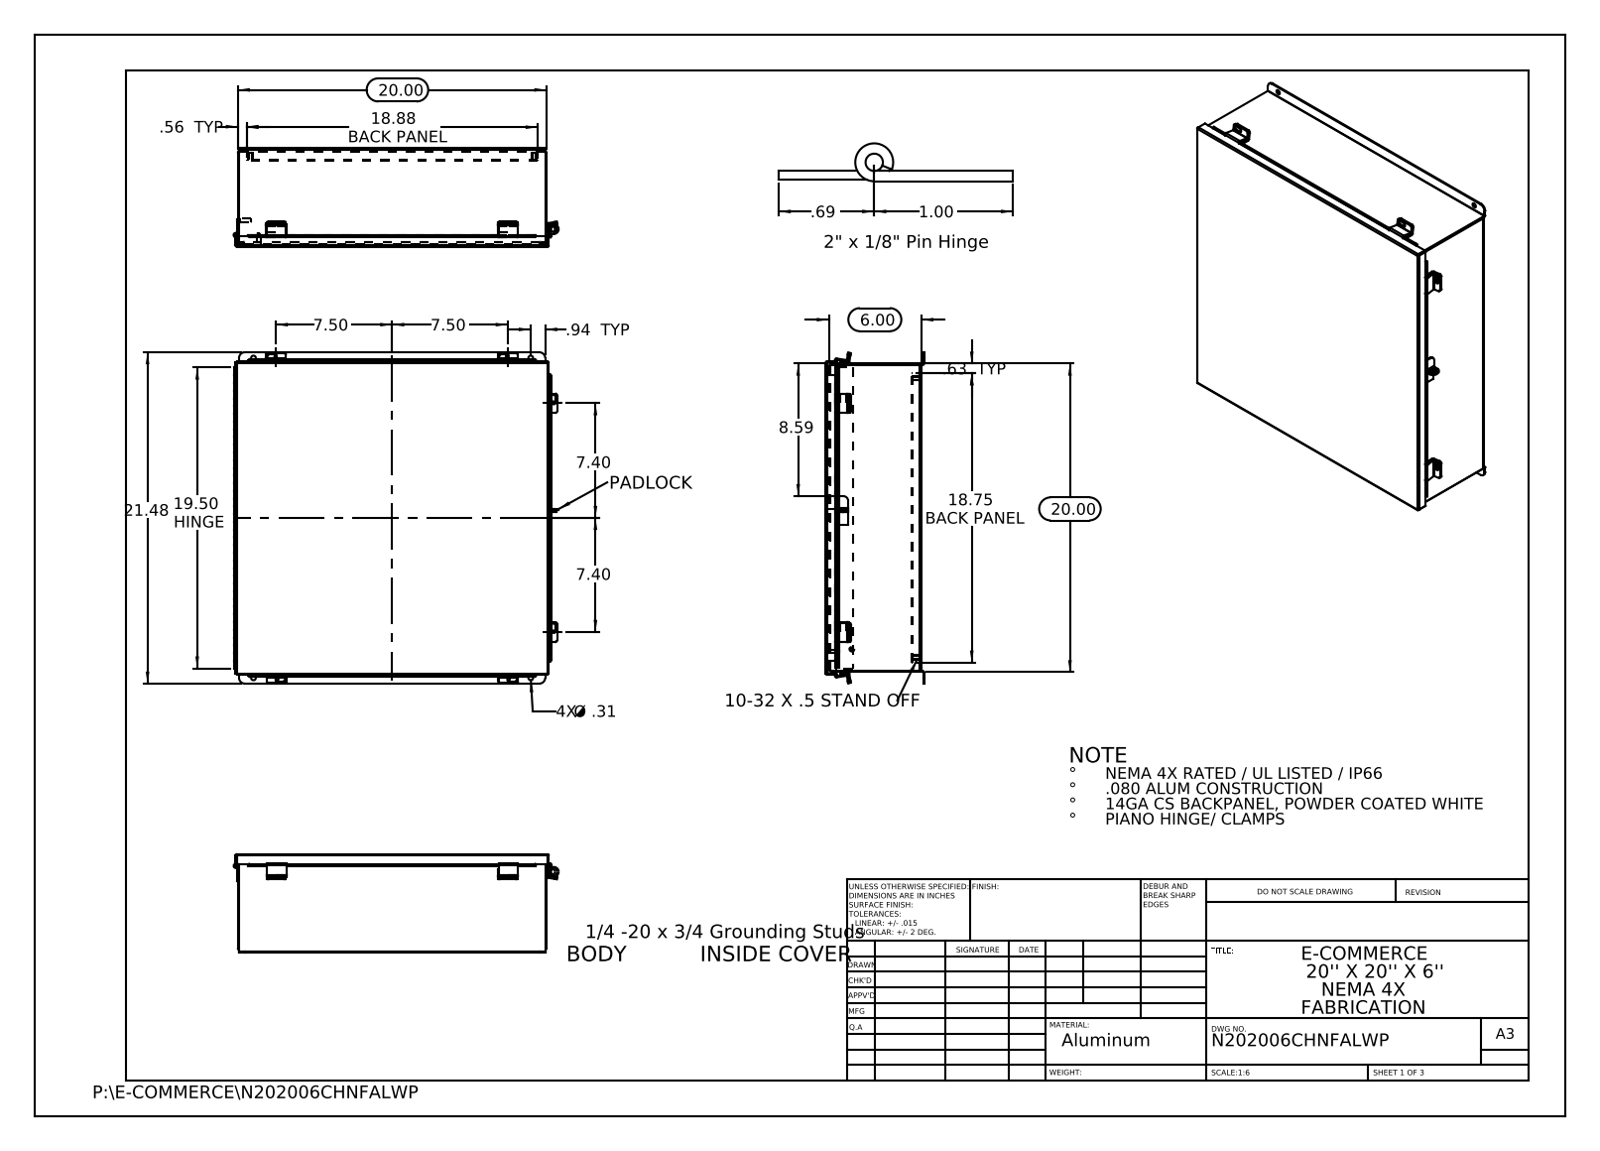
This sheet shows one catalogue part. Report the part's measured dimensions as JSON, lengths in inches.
{"part_name": "N202006CHNFALWP JIC Bottom; N202006CHNFALWP JIC Cover Clamp; N202006CHNFALWP Hinge Body Side; N202006CHNFALWP _JIC Hinge (+8 more)", "step_written_by": "SolidWorks 2013 (CONFIG_CONTROL_DESIGN)", "units": "inches", "bodies": {"solids": 27, "faces": 938, "planar": 579, "cylindrical": 339, "other": 20}, "overall_size": [21.476, 21.072, 6.39], "volume_in3": 135.3, "surface_area_in2": 3669, "round_holes": [[0.25, 10], [0.187, 4], [0.312, 4], [0.125, 1], [0.125, 1], [0.373, 1], [0.375, 1]], "round_bosses_or_shafts": [[0.313, 4], [0.315, 2], [0.236, 2], [0.273, 1], [0.25, 1]], "partial_cylinders_radius": [[0.125, 21], [0.013, 13], [0.009, 12], [0.088, 12], [0.133, 12], [0.083, 6], [0.1, 6], [0.375, 4]], "face_to_face_distances": [0.075, 6.128, 19.925, 6.053, 6.203, 0.074, 5.628, 0.575, 0.5, 5.553], "hole_center_spacings": [1.315, 18.222, 19.427, 26.603, 15, 17.976, 18.126, 18.375]}
